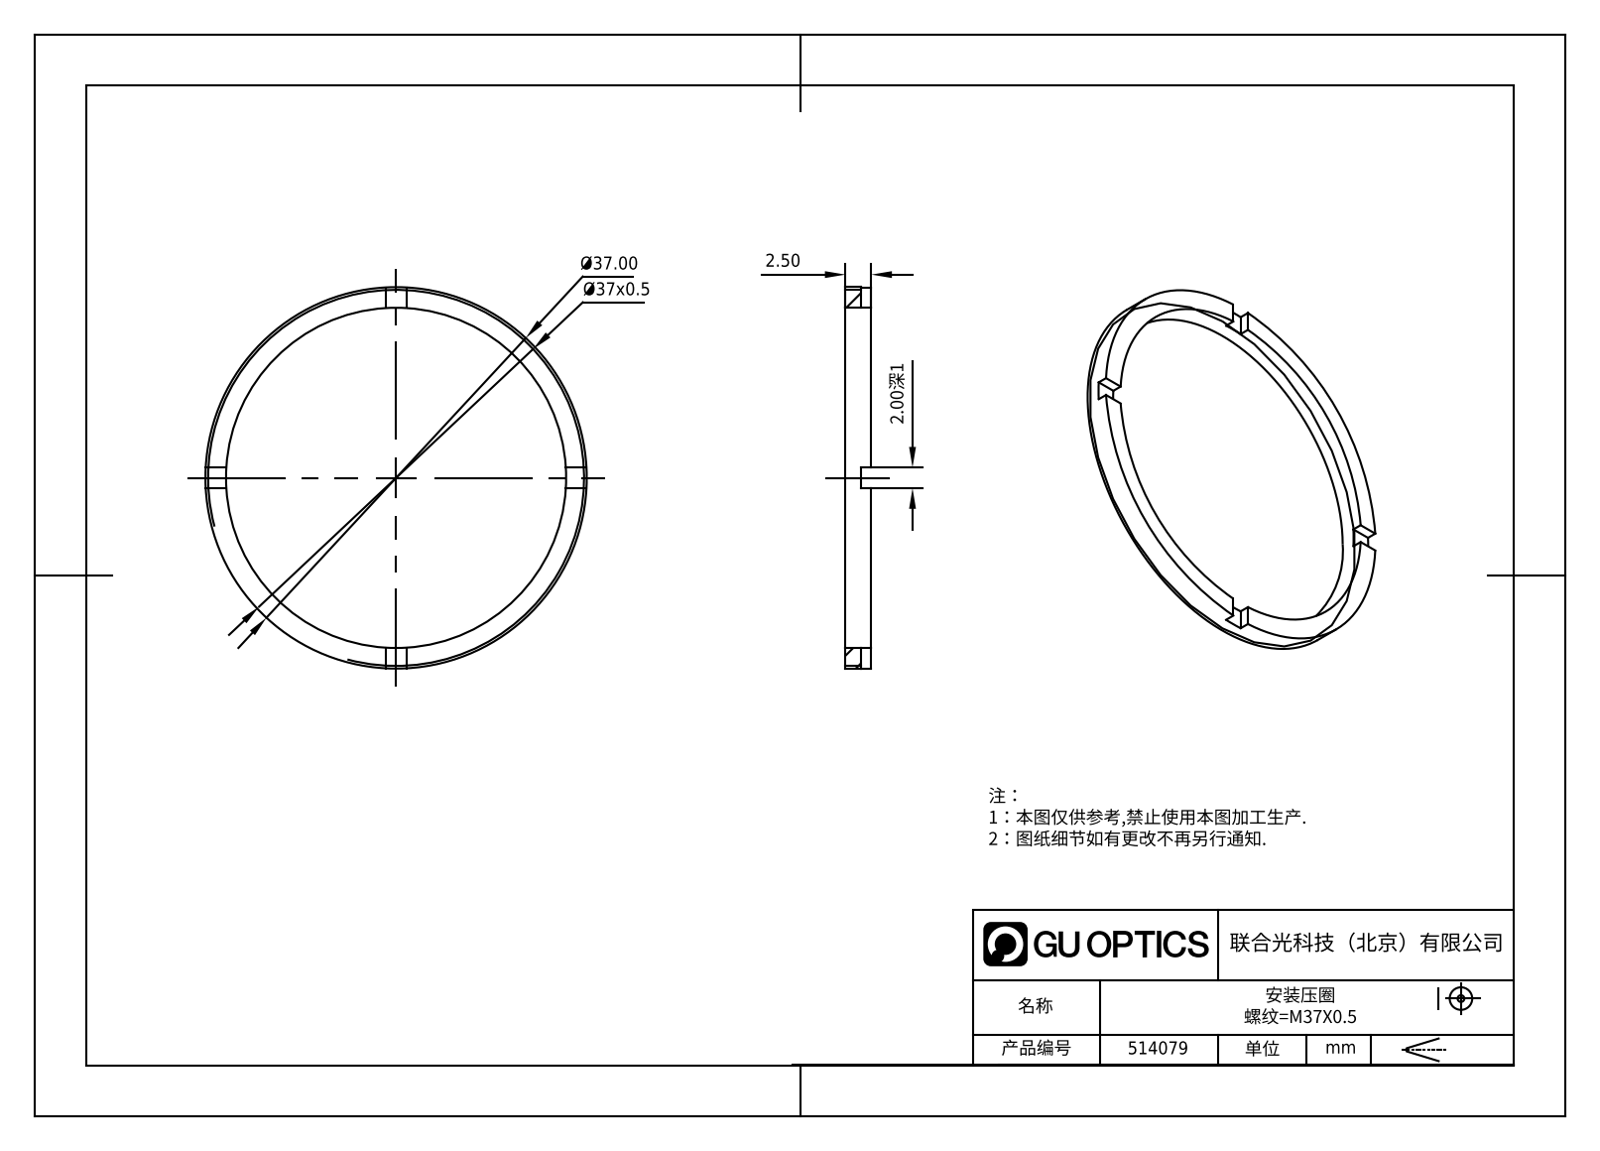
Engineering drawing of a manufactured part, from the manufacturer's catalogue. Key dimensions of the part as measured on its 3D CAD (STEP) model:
Part name (STEP PRODUCT): 514079
STEP written by: SolidWorks 2020 (CONFIG_CONTROL_DESIGN)
Units: millimetres
Bodies: 1 solid, 21 faces (17 planar, 4 cylindrical, 0 other)
Overall size (bounding box): 37 × 37 × 2.5
Volume: 534 mm³ · Surface area: 990 mm²
Round holes (diameter × count): ⌀33 ×1
Round bosses / shafts (diameter × count): ⌀37 ×1
Main face-to-face distances: 2.5, 1.5, 1, 2
